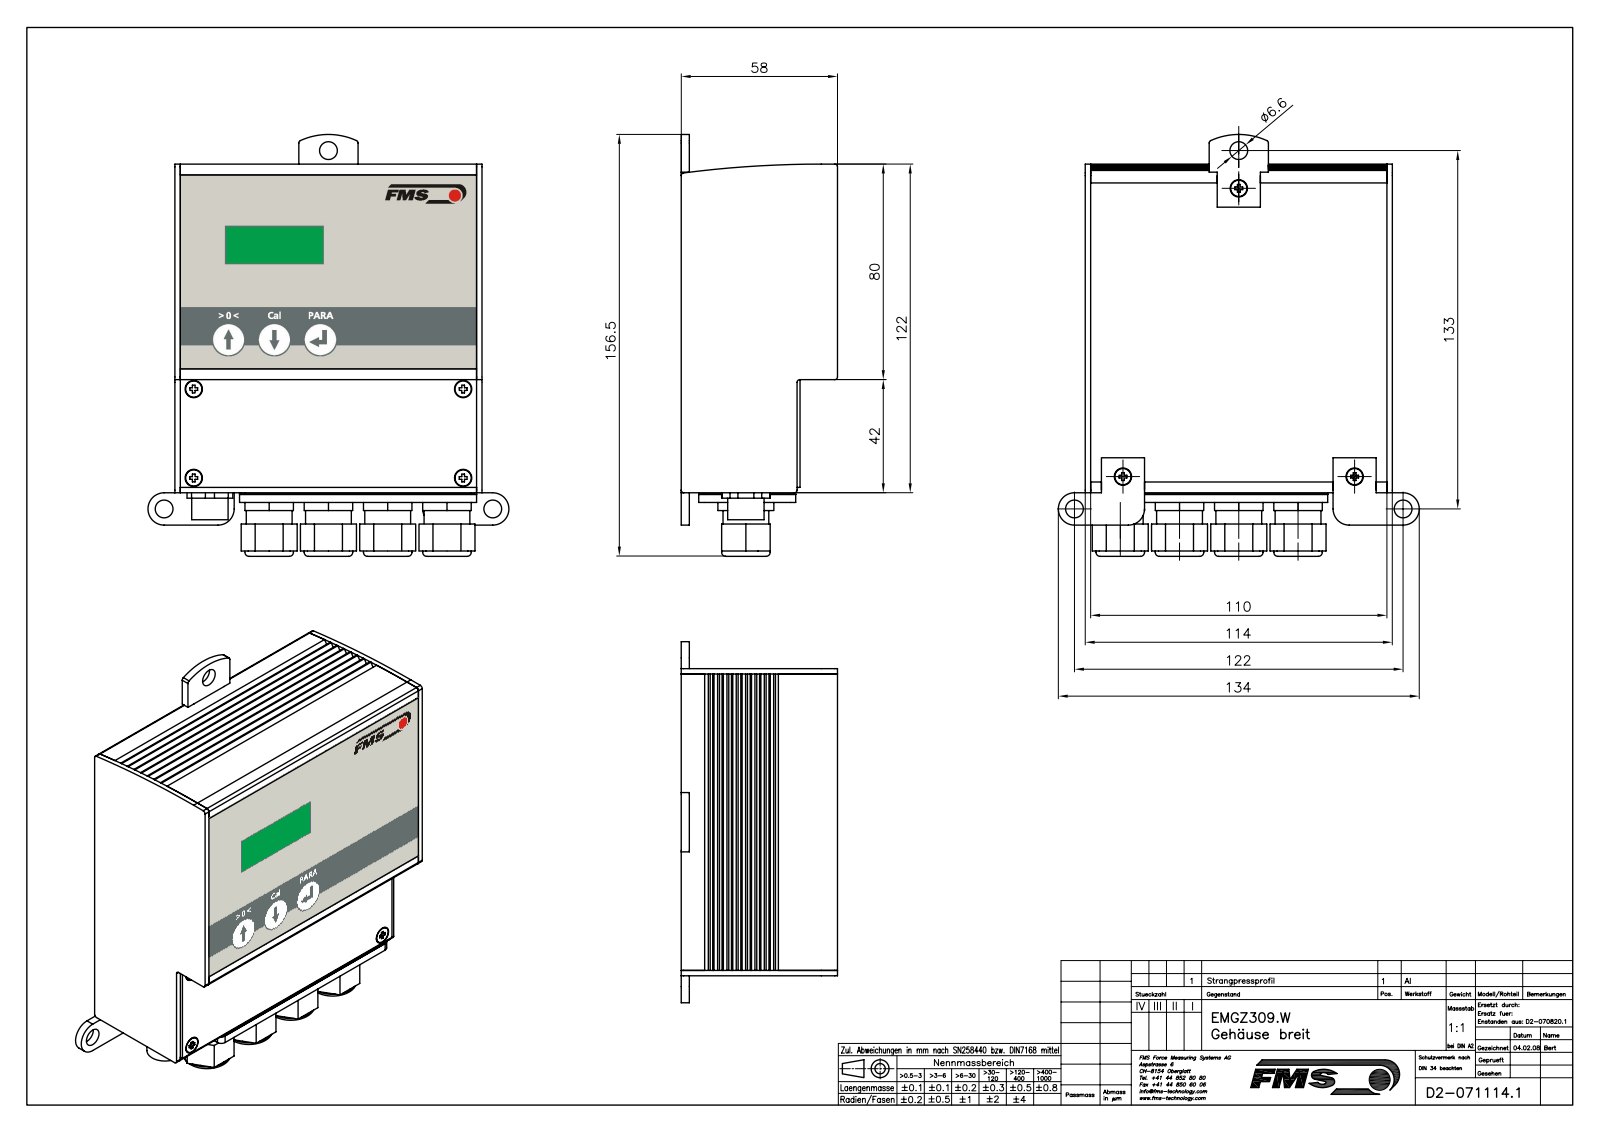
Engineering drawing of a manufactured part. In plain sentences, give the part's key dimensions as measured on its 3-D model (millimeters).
The part is named "E0711141; E0711142; E0708103; E0708203 (+7 more)". Its 3-D file was written by "Mechanical Desktop 2009 (CONFIG_CONTROL_DESIGN)". It is 41 solids with 1881 faces: 1301 planar, 408 cylindrical and 172 other. Overall it measures 156.5 by 134 by 58 millimeters. Its volume is 222 523 cubic millimeters and its surface area 190 990 square millimeters. Round holes: 16 of diameter 3, 12 of diameter 2.6, 11 of diameter 3.2, 5 of diameter 14.68, 4 of diameter 1, 4 of diameter 2.4, 4 of diameter 10, 4 of diameter 11, 4 of diameter 12, 4 of diameter 13.5, 4 of diameter 16, 4 of diameter 16.15. Round bosses or shafts: 12 of diameter 3, 11 of diameter 6, 5 of diameter 16, 4 of diameter 18, 4 of diameter 17, 4 of diameter 15.5, 2 of diameter 2.67, 1 of diameter 13.5. Partial cylindrical surfaces (rounded edges, fillets, slot ends): 19 of radius 0.25, 12 of radius 1, 6 of radius 4, 4 of radius 0.1, 4 of radius 0.36, 4 of radius 2, 4 of radius 5, 4 of radius 6. The main face-to-face distances are 2, 3, 2.5, 112, 28, 0.5, 42, 12.5, 6, 30. The hole center spacings are 8.63, 3.5, 9.95, 7, 12.16, 10.5, 44, 14.
